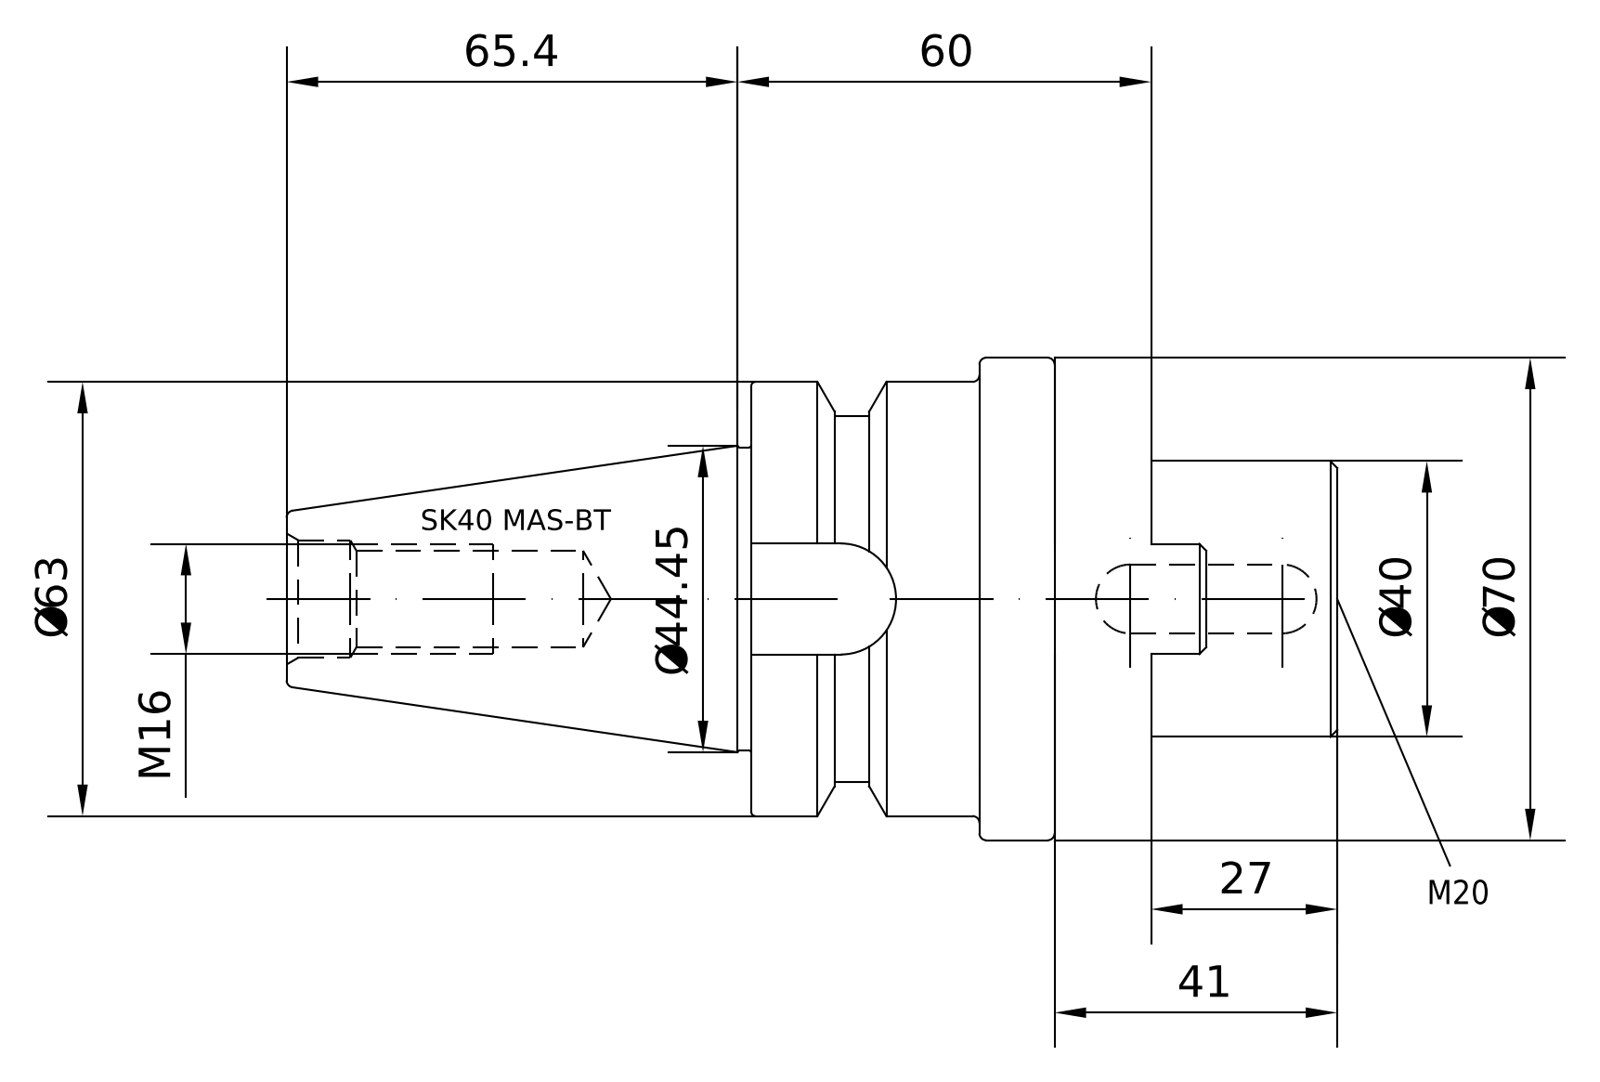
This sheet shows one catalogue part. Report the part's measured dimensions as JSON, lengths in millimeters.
{"part_name": "40-540-40; 85-200-40; 40-540-40_ASM", "step_written_by": "PRO/ENGINEER BY PARAMETRIC TECHNOLOGY CORPORATION, 2010430 (CONFIG_CONTROL_DESIGN)", "units": "millimeters", "bodies": {"solids": 2, "faces": 195, "planar": 93, "cylindrical": 40, "other": 62}, "overall_size": [162.4, 70, 70], "volume_mm3": 291282, "surface_area_mm2": 51759, "round_holes": [[13.84, 1], [17.01, 1], [17.5, 1], [20, 1], [40.39, 1], [45, 1]], "round_bosses_or_shafts": [[70, 1], [62.98, 1], [59, 1], [52.75, 1], [43.75, 1], [40, 1], [16.01, 1]], "partial_cylinders_radius": [[5, 2], [8.05, 1], [8.1, 1]], "face_to_face_distances": [14, 54, 68, 95, 41, 27, 12, 1, 13, 43]}
